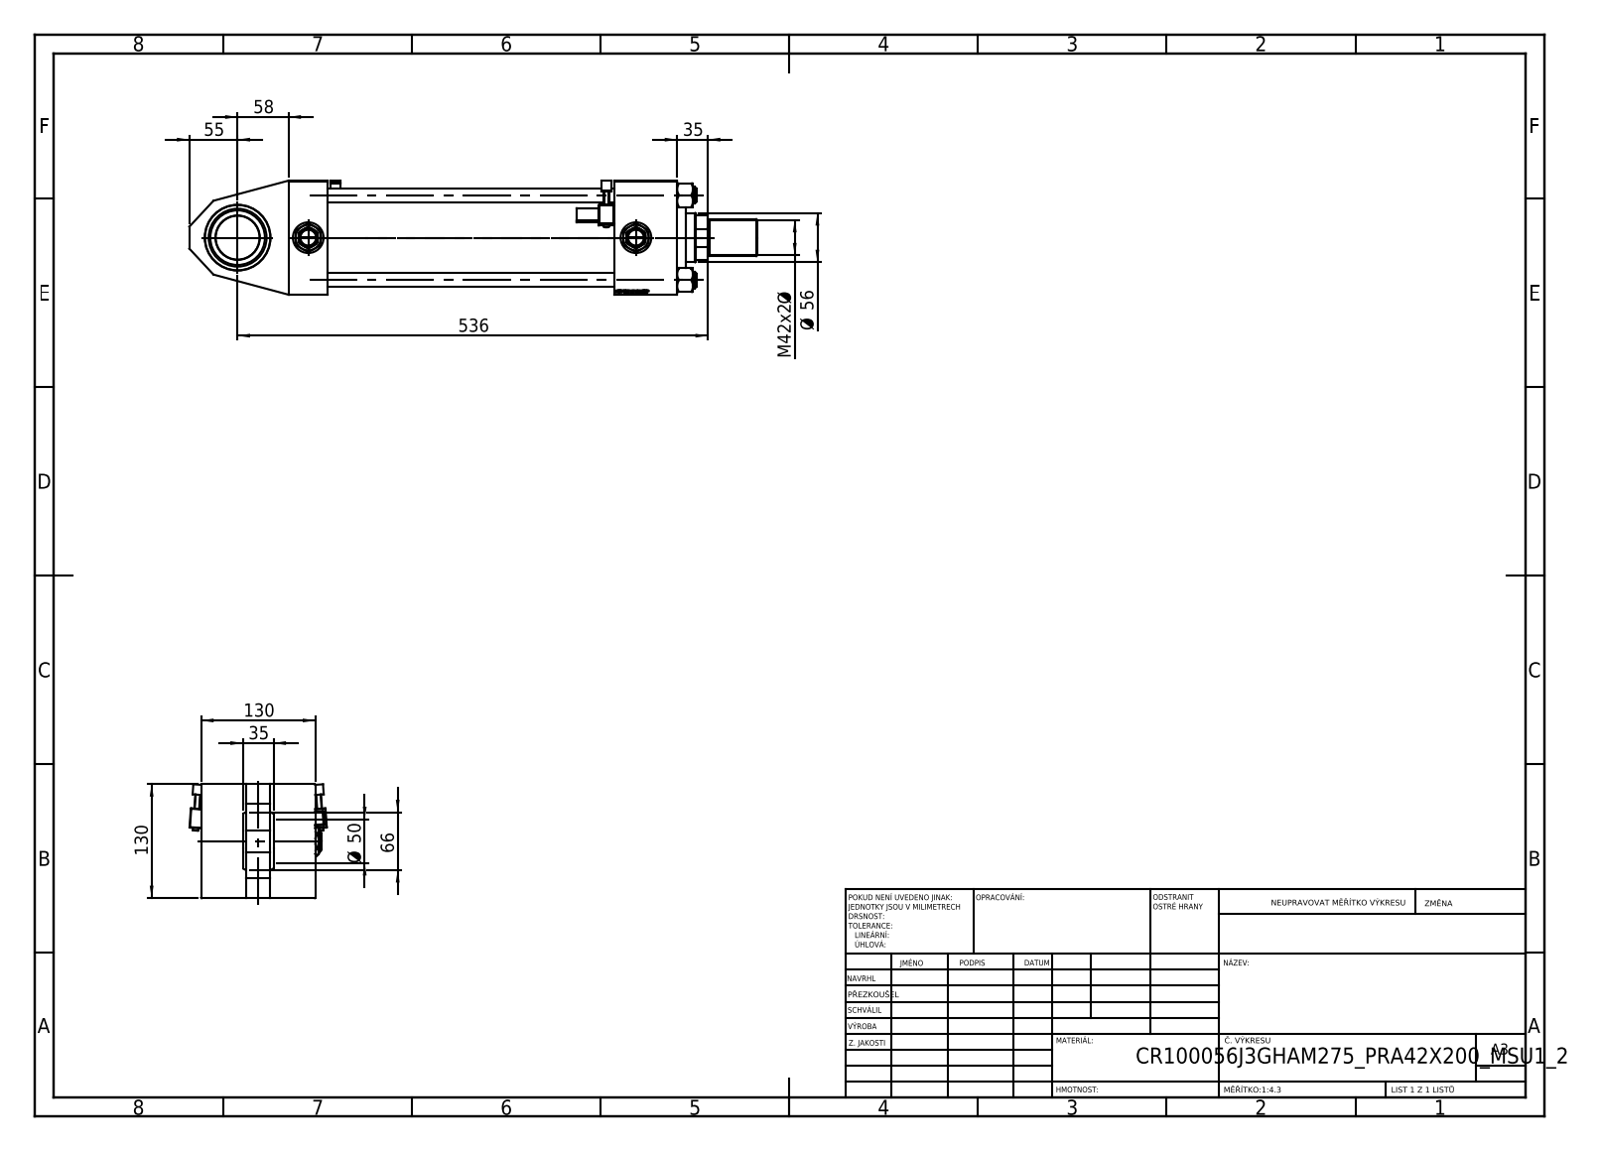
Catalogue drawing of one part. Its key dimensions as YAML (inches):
part_name: "V215CR_J_VNITRNI_KROUZEK; V215CR_VCP_J; V215CR_MSU; V215CR_TYCINKA_J (+5 more)"
step_written_by: "SolidWorks 2019 (CONFIG_CONTROL_DESIGN)"
units: inches
bodies: {solids: 17, faces: 1462, planar: 674, cylindrical: 164, other: 624}
overall_size: [25.472, 6.157, 5.118]
volume: 240.2
surface_area: 1039
round_holes:
  - {diameter: 0.63, count: 4}
  - {diameter: 0.098, count: 2}
  - {diameter: 0.276, count: 2}
  - {diameter: 1.041, count: 2}
  - {diameter: 1.378, count: 2}
  - {diameter: 1.594, count: 1}
  - {diameter: 1.969, count: 1}
  - {diameter: 2.205, count: 1}
  - {diameter: 2.323, count: 1}
  - {diameter: 2.953, count: 1}
  - {diameter: 2.992, count: 1}
  - {diameter: 3.366, count: 1}
round_bosses_or_shafts:
  - {diameter: 0.748, count: 4}
  - {diameter: 0.236, count: 2}
  - {diameter: 4.173, count: 1}
  - {diameter: 2.835, count: 1}
  - {diameter: 1.654, count: 1}
  - {diameter: 1.575, count: 1}
partial_cylinders:
  - {radius: 0.02, count: 48}
  - {radius: 0.039, count: 2}
  - {radius: 0.098, count: 2}
  - {radius: 0.157, count: 2}
  - {radius: 1.063, count: 1}
face_to_face_distances: [5.118, 2.008, 3.11, 1.772, 17.441, 15.669, 14.606, 12.835, 2.835, 1.102]
hole_center_spacings: [1.93, 2.698, 3.815, 4.005, 1.614, 5.395, 3.169, 3.228]
